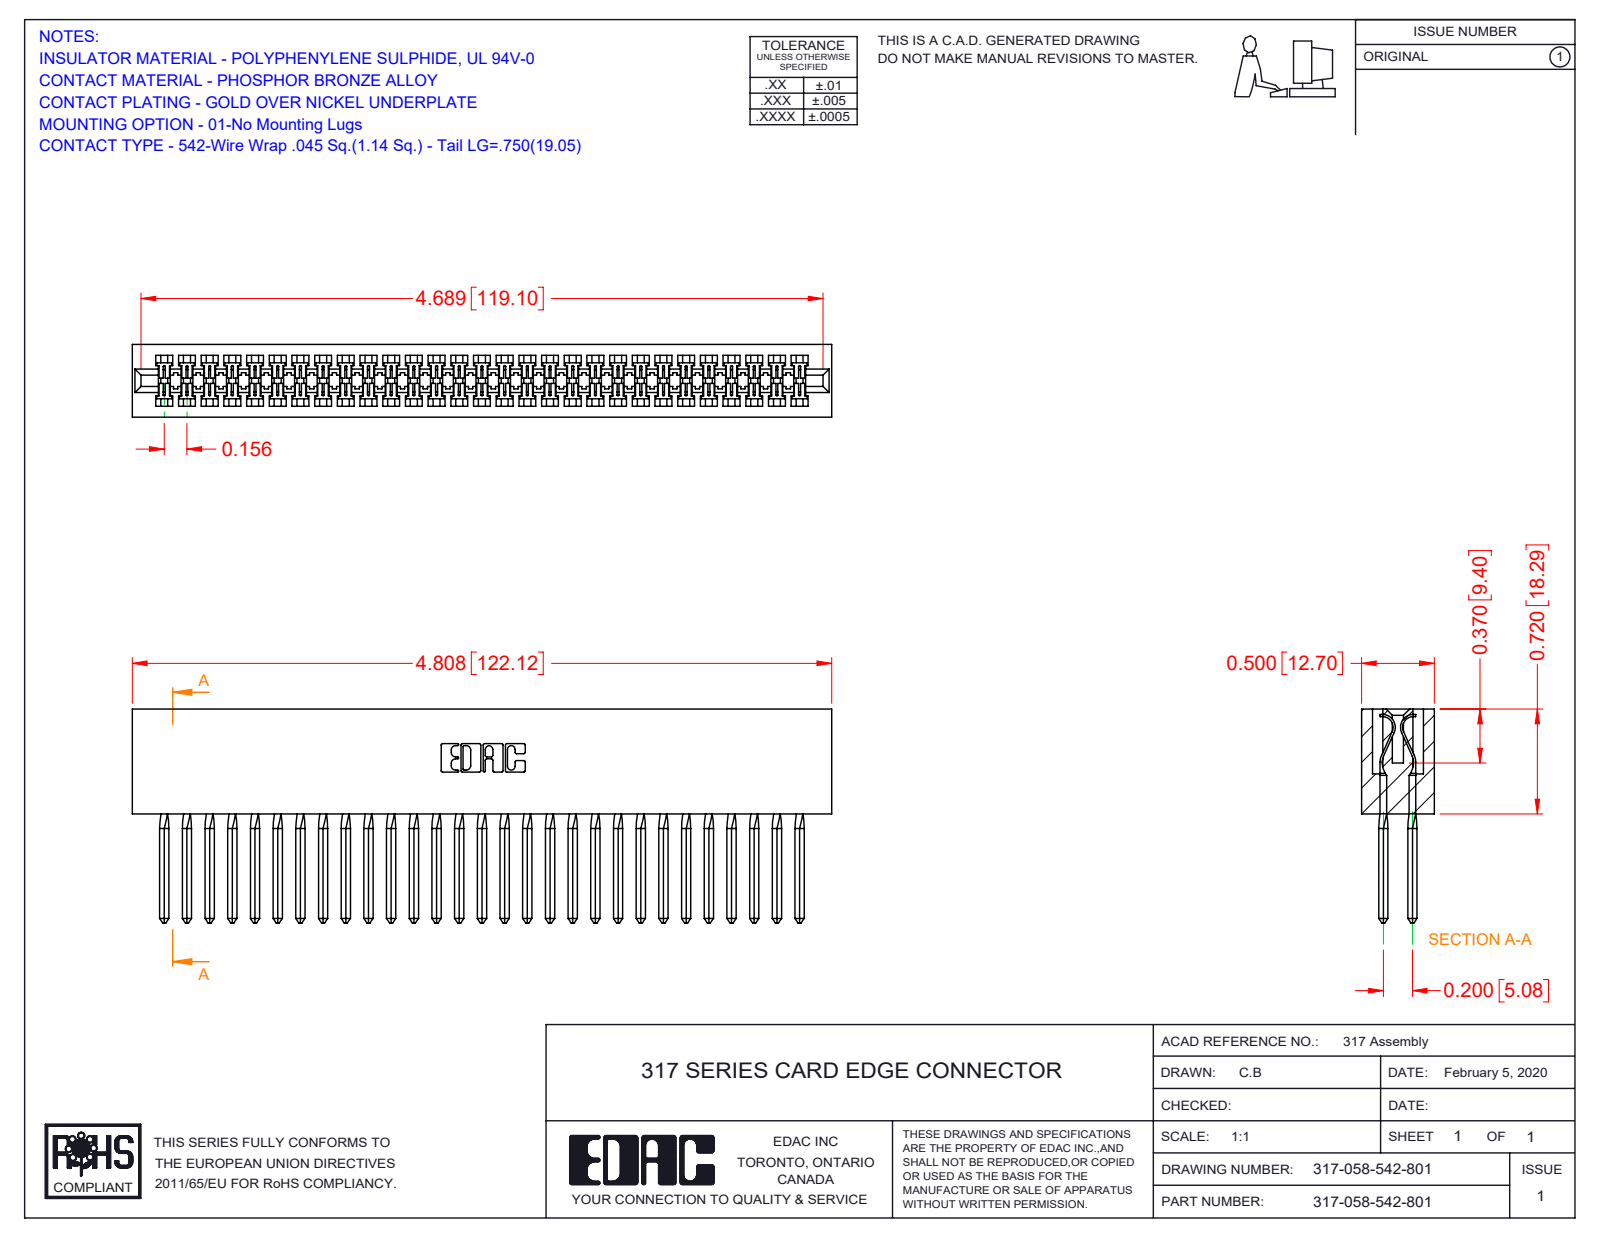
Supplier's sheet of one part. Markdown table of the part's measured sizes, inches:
| quantity | value |
| --- | --- |
| part name | 317-058-542-801; 317 Part_Lugless; 317-290-003_542 |
| STEP written by | SolidWorks 2016 (CONFIG_CONTROL_DESIGN) |
| units | inches |
| bodies | 59 solids, 3396 faces (2718 planar, 446 cylindrical, 232 other) |
| overall size | 4.808 × 1.47 × 0.5 |
| volume | 1.301 in³ |
| surface area | 45.57 in² |
| partial cylindrical surfaces (radius × count) | 0.006 × 116, 0.01 × 22, 0.007 × 6, 0.031 × 6, 0.026 × 3, 0.074 × 2, 0.089 × 2, 0.1 × 2 |
| main face-to-face distances | 0.5, 0.075, 0.425, 0.35, 0.2, 0.116, 0.11, 0.046, 0.128, 0.372 |
